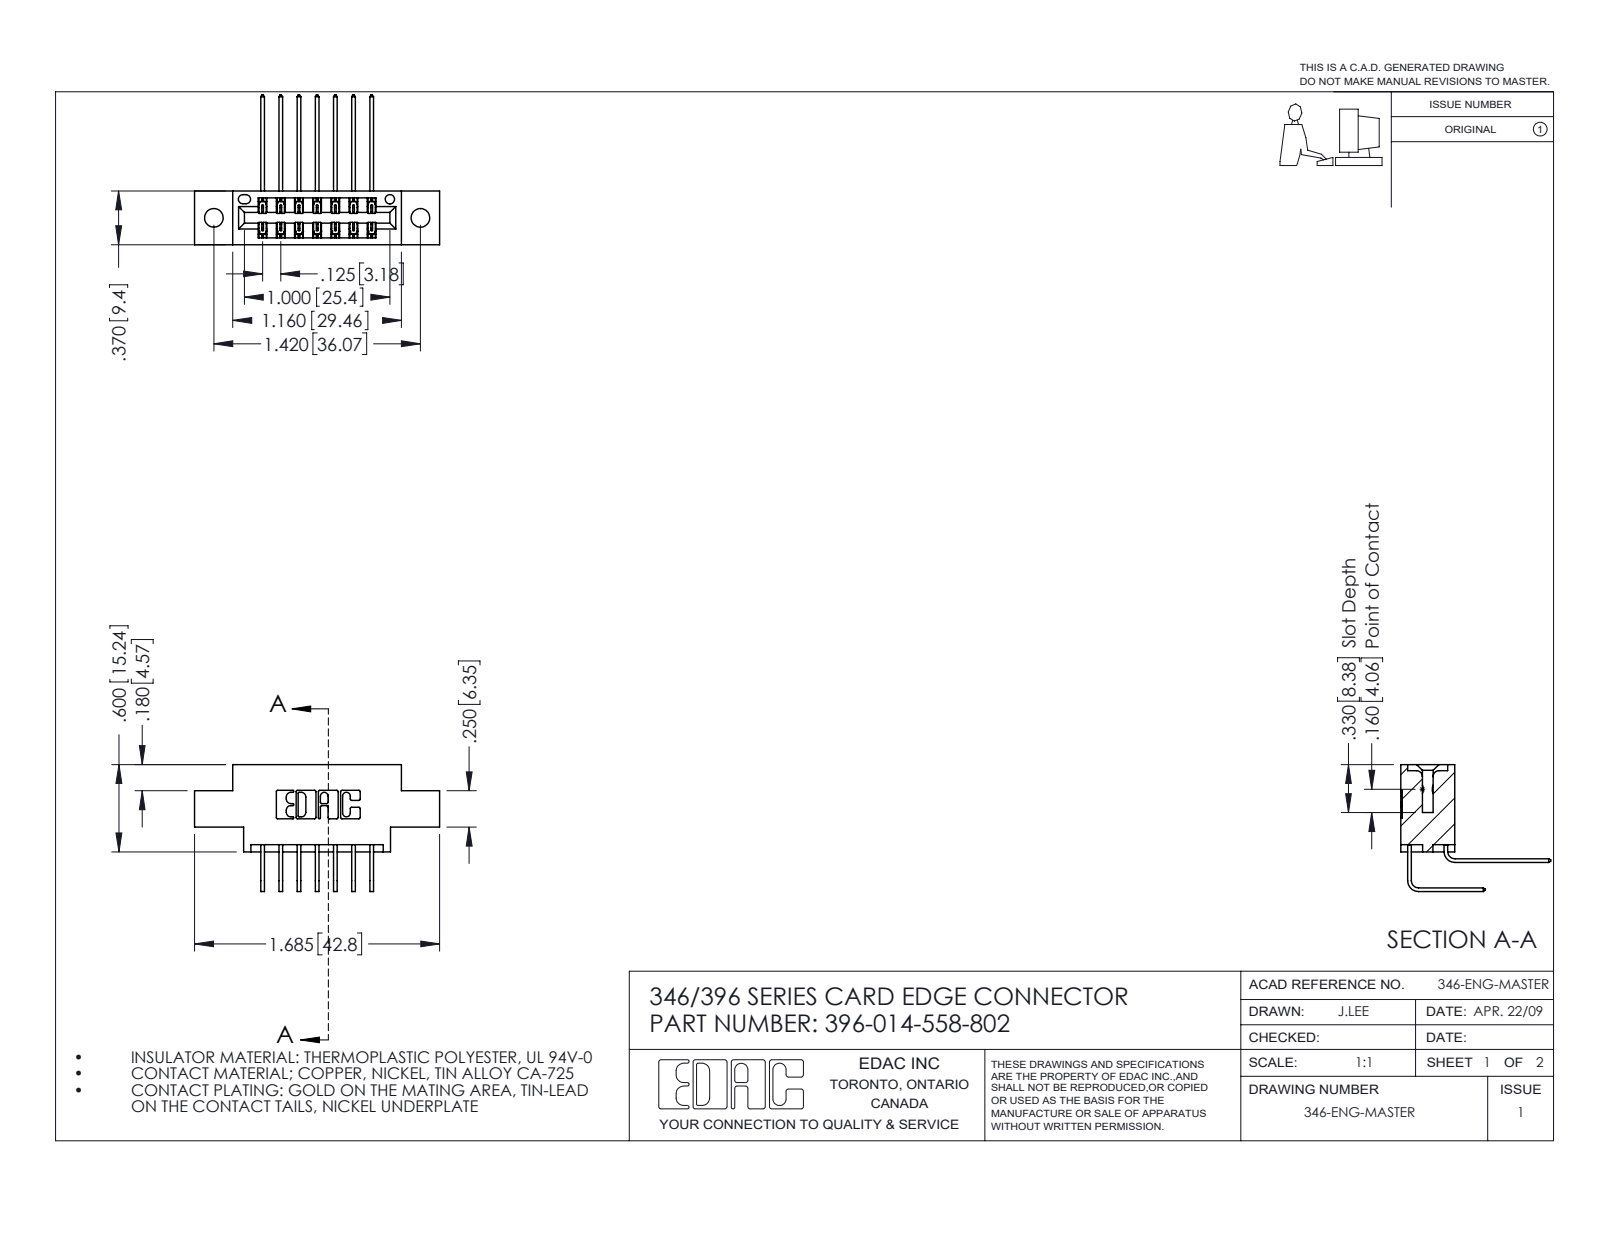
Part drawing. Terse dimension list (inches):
name: 345-292-001_558 559 Tail - 1; 346 Part_0.170 Offset - 0.128 Dia; 396-014-558-802; 345-292-001_558 Tail - 2
written by: SolidWorks 2016 (CONFIG_CONTROL_DESIGN)
unit: in
bodies: 15 solids, 882 faces (598 planar, 284 cylindrical, 0 other)
size: 1.685 × 1.03 × 0.873
volume: 0.231 in³; area: 7.686 in²
holes: 2× ⌀0.128, 1× ⌀0.064
rounds: 22× R0.01, 21× R0.006, 6× R0.007, 6× R0.031, 3× R0.026, 2× R0.014, 2× R0.022, 2× R0.024
face distances: 0.25, 0.37, 0.048, 0.322, 0.025, 0.072, 0.298, 0.148, 0.222, 0.1
hole spacings: 0.246, 1.217, 1.42
